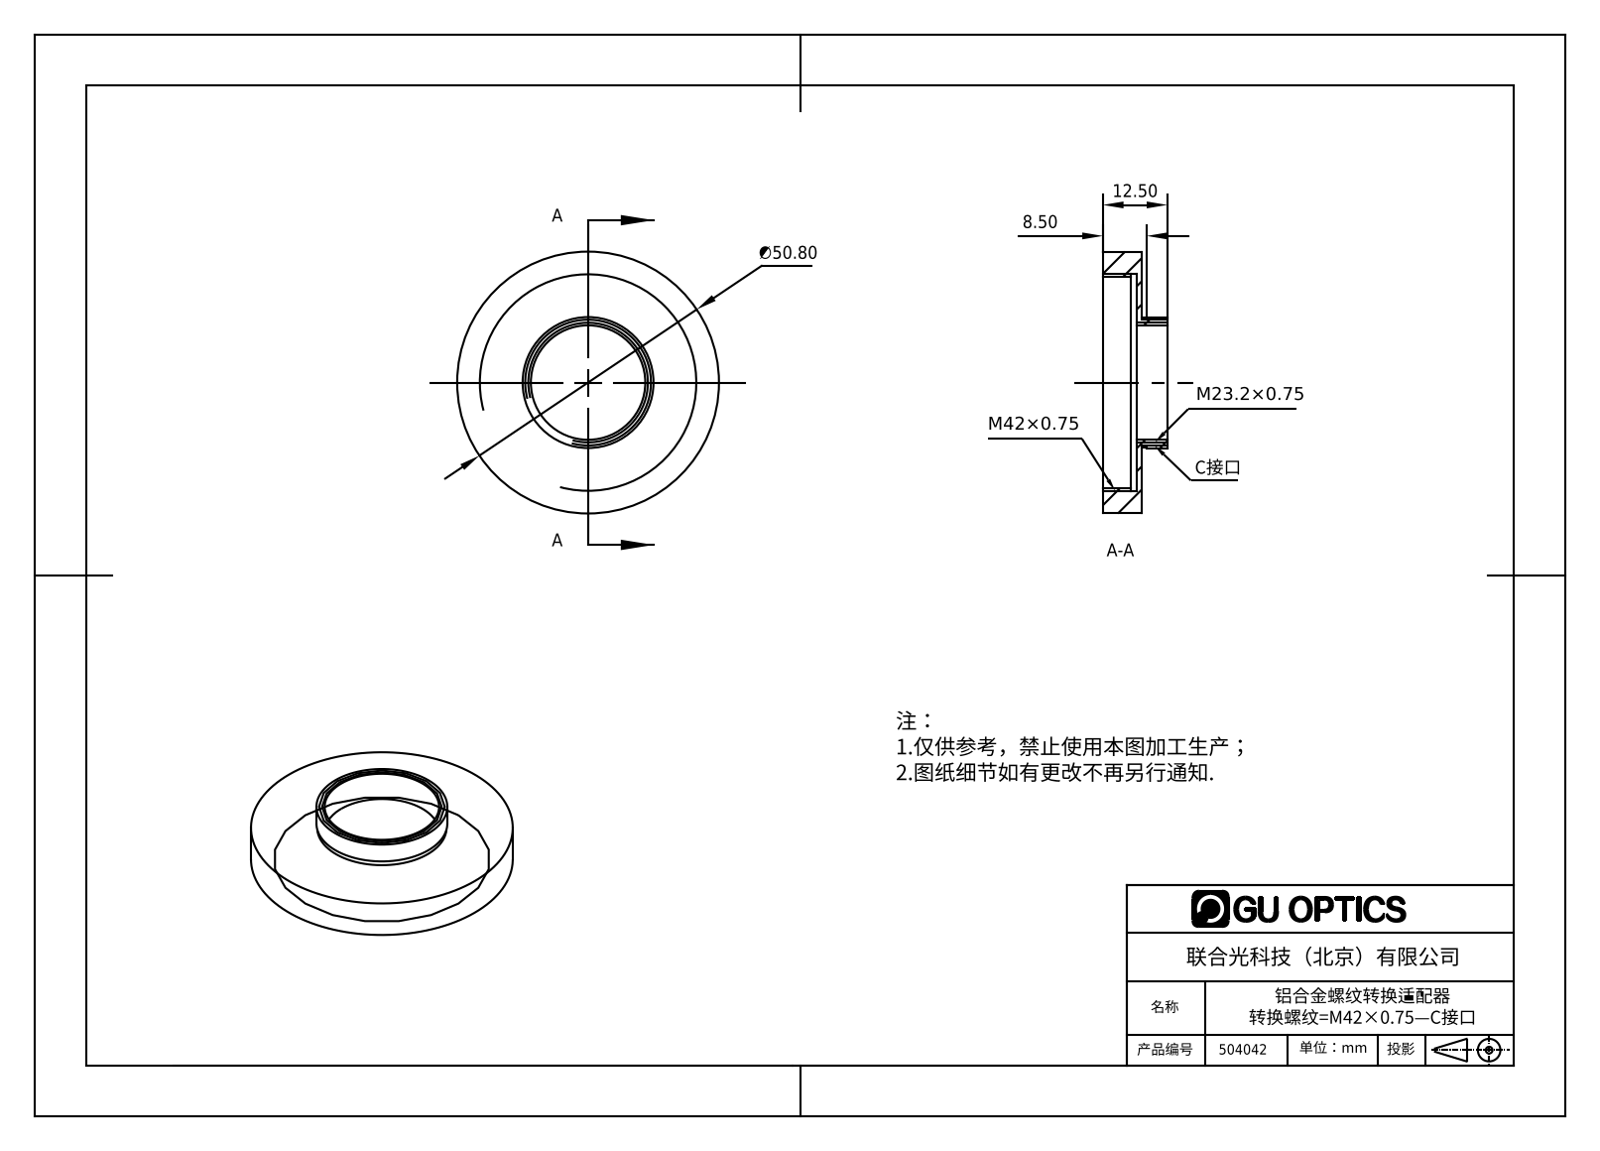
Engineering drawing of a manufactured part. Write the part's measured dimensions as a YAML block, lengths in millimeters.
part_name: "504042"
step_written_by: "SolidWorks 2016 (AUTOMOTIVE_DESIGN)"
units: millimeters
bodies: {solids: 1, faces: 18, planar: 6, cylindrical: 12, other: 0}
overall_size: [50.8, 50.8, 12.5]
volume: 6740
surface_area: 6315
round_holes:
  - {diameter: 22.2, count: 1}
  - {diameter: 41, count: 1}
  - {diameter: 42.2, count: 1}
round_bosses_or_shafts:
  - {diameter: 50.8, count: 1}
  - {diameter: 25.4, count: 1}
  - {diameter: 25.1, count: 1}
face_to_face_distances: [1, 6.5, 7.5, 12.5, 6, 5, 2, 5.5, 7, 8.5]
